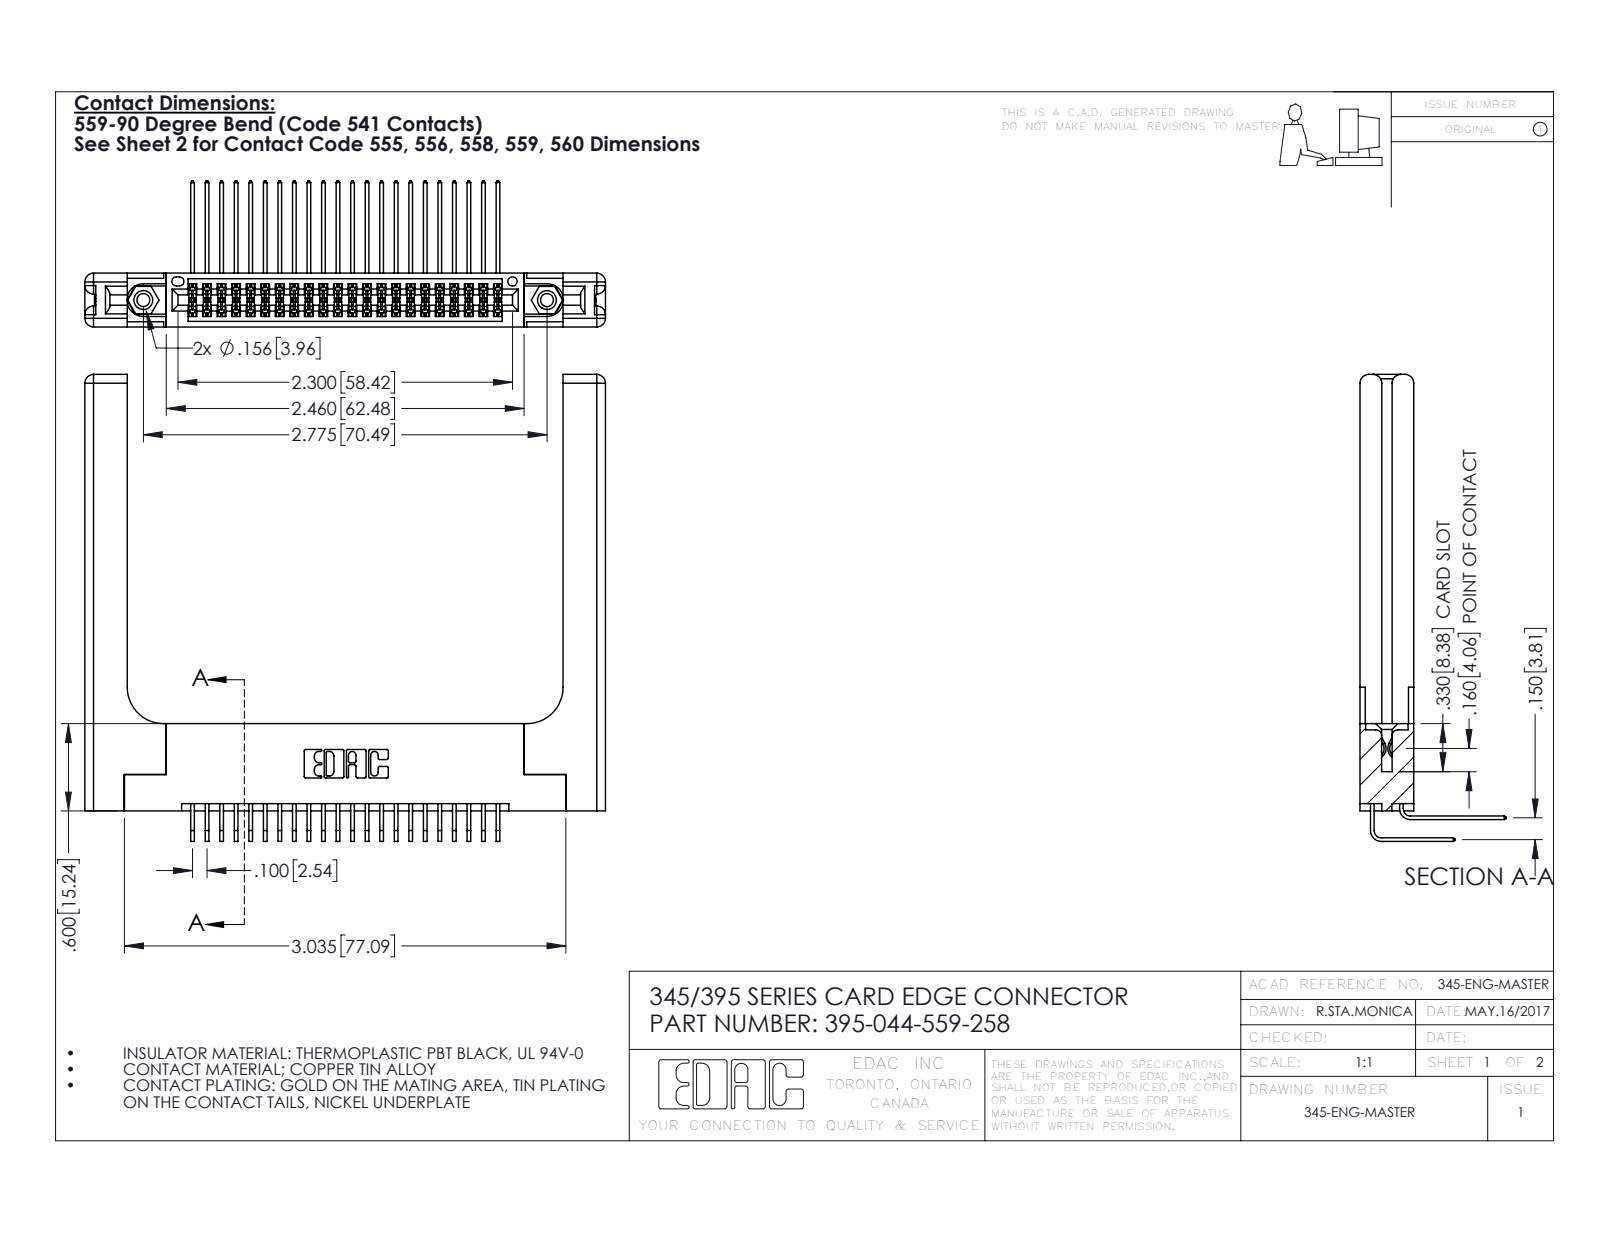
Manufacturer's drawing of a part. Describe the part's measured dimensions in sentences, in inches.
The part is named "395-044-559-258; 345-250-001_345-250-001-102; 345-292-001_558 559 Tail - 1; 345-220-058_345-220-058 (+2 more)". Its 3-D file was written by "SolidWorks 2016 (CONFIG_CONTROL_DESIGN)". It is 49 solids with 2670 faces: 1768 planar, 842 cylindrical and 60 other. Overall it measures 3.579 by 3.209 by 1.005 inches. Its volume is 1.06 cubic inches and its surface area 29.48 square inches. Round holes: 2 of diameter 0.089, 2 of diameter 0.125, 2 of diameter 0.156, 1 of diameter 0.064. Round bosses or shafts: 2 of diameter 0.155. Partial cylindrical surfaces (rounded edges, fillets, slot ends): 67 of radius 0.006, 22 of radius 0.01, 16 of radius 0.06, 6 of radius 0.007, 6 of radius 0.031, 3 of radius 0.026, 2 of radius 0.014, 2 of radius 0.019. The main face-to-face distances are 0.37, 0.072, 0.298, 0.2, 0.15, 0.148, 0.077, 0.098, 0.272, 0.025. The hole center spacings are 0.27, 2.541, 2.775.
